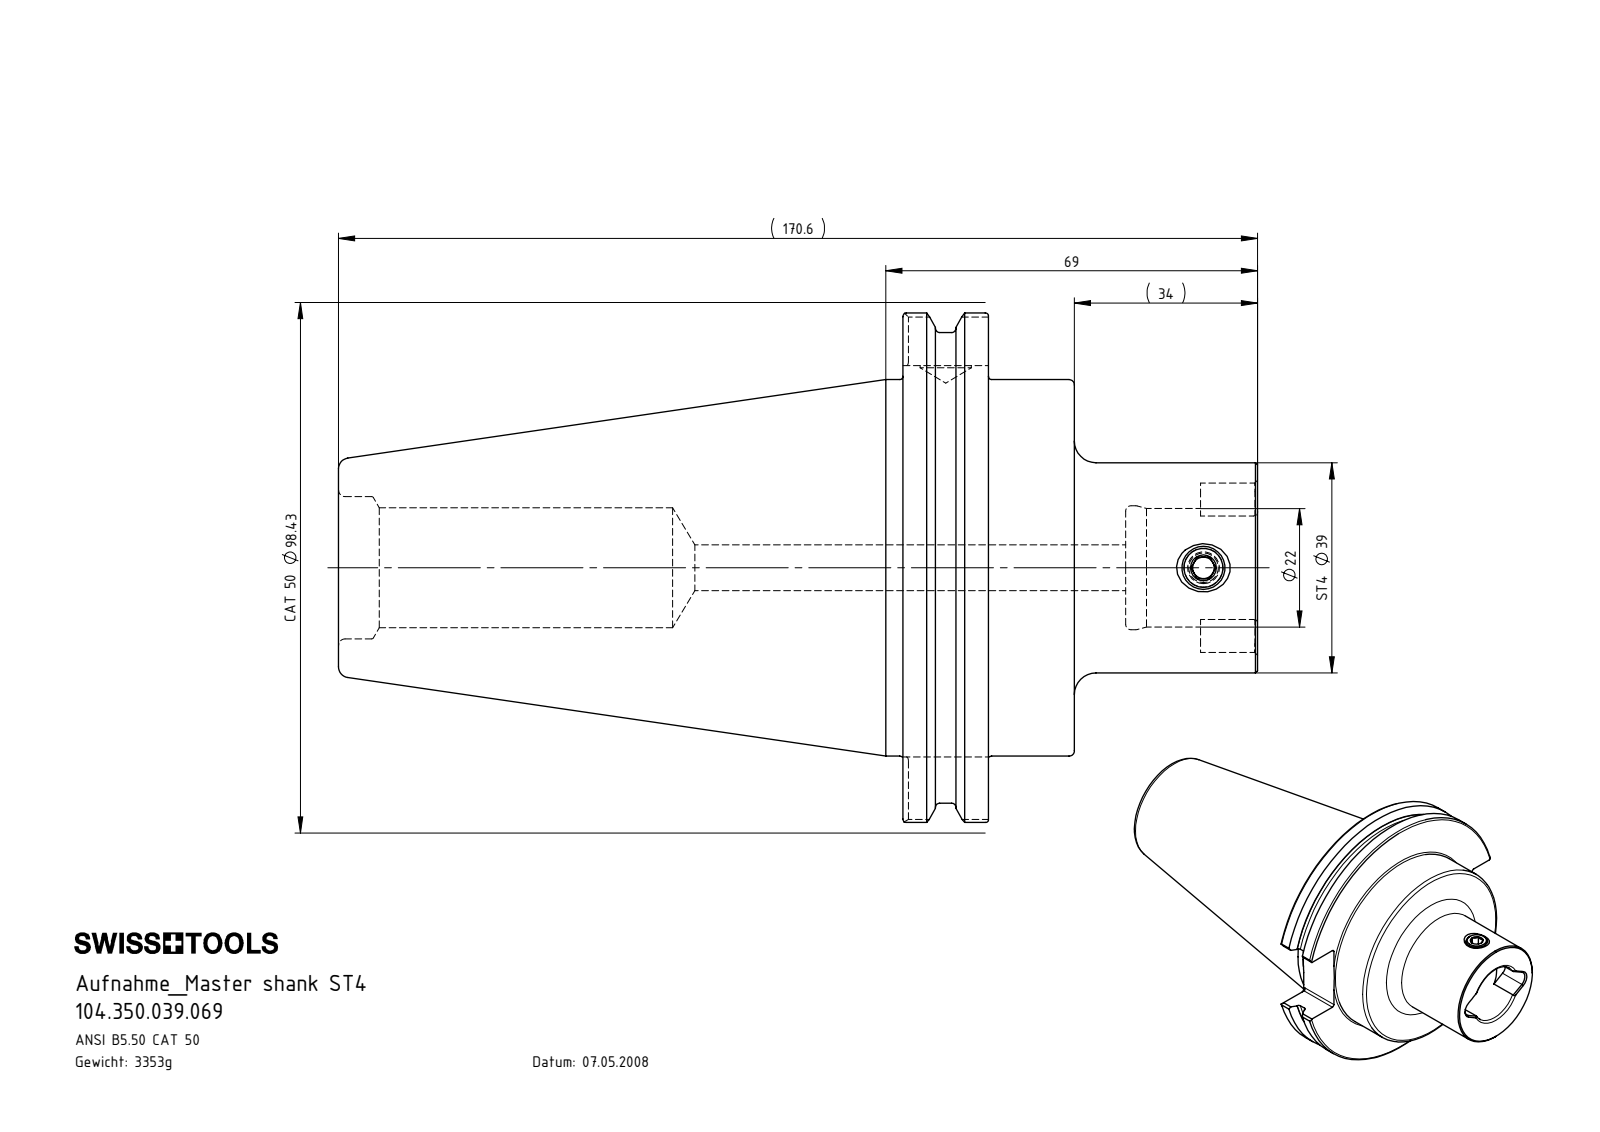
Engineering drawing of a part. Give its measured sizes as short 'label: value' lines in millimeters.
name: CT5-ST4.K01.069; ST4-ER1.001.011_A; CT5-ST4.K01.069_A
written by: SolidWorks 2015 (CONFIG_CONTROL_DESIGN)
unit: mm
bodies: 2 solids, 140 faces (44 planar, 39 cylindrical, 57 other)
size: 170.6 × 98.42 × 94.52
volume: 427 133 mm³; area: 51 993 mm²
holes: 1× ⌀7.25, 1× ⌀8.5, 1× ⌀9.5, 1× ⌀22, 1× ⌀22.25, 1× ⌀23, 1× ⌀26.4
bosses: 1× ⌀98.42, 1× ⌀91, 1× ⌀69.85, 1× ⌀39, 1× ⌀8
rounds: 8× R0.8, 2× R3.2
face distances: 15.87, 31.82, 15.95, 65.82, 49.95, 34, 104.78, 120.65, 136.6, 170.6
